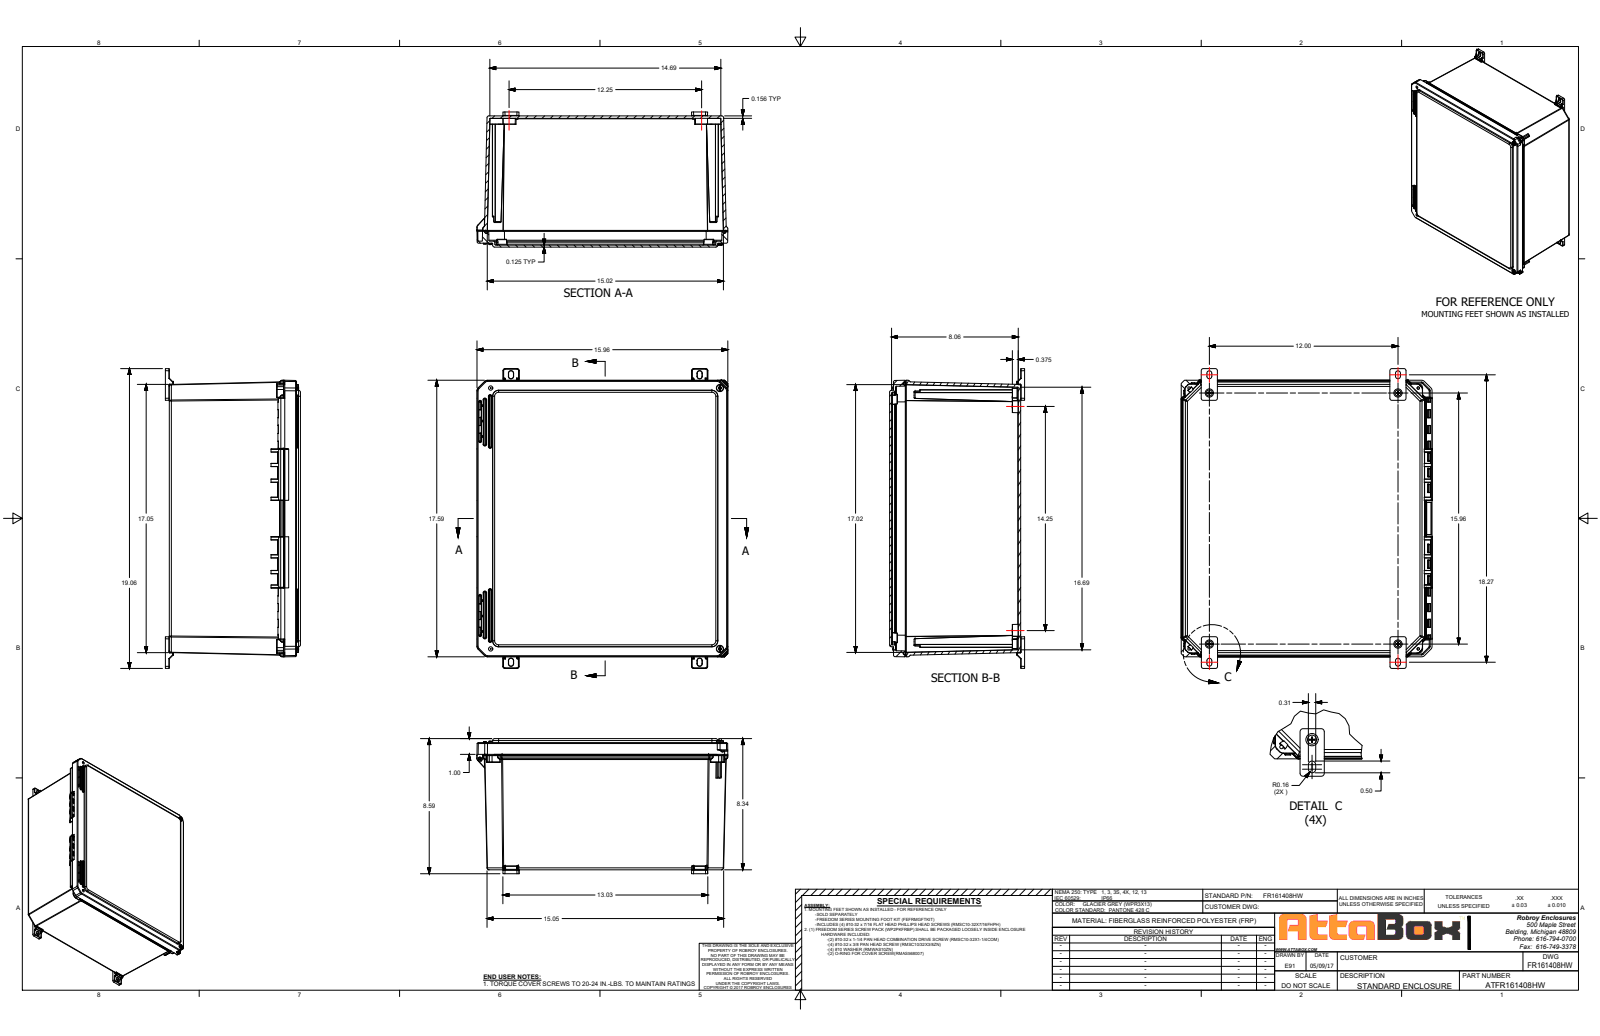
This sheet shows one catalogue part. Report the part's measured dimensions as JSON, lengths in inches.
{"part_name": "FR161408HW", "step_written_by": "SolidWorks 2021 (AUTOMOTIVE_DESIGN)", "units": "inches", "bodies": {"solids": 8, "faces": 2143, "planar": 663, "cylindrical": 835, "other": 645}, "overall_size": [17.586, 15.962, 8.341], "volume_in3": 184, "surface_area_in2": 2213, "round_holes": [[0.152, 8], [0.252, 4], [0.253, 4], [0.219, 2], [0.227, 2], [0.313, 2], [0.137, 1], [0.156, 1]], "round_bosses_or_shafts": [[0.45, 2], [0.435, 2], [0.199, 2], [0.262, 1], [0.135, 1], [0.135, 1]], "partial_cylinders_radius": [[0.01, 176], [0.005, 80], [0.02, 57], [0.03, 45], [0.03, 24], [0.09, 24], [0.096, 24], [0.125, 22]], "face_to_face_distances": [0.125, 0.156, 8.185, 8.341, 8.217, 8.061, 0.18, 0.181, 0.181, 0.179], "hole_center_spacings": [15.461, 16.324, 15.899, 20.438, 0.865, 1.33, 13.296, 15.106]}
